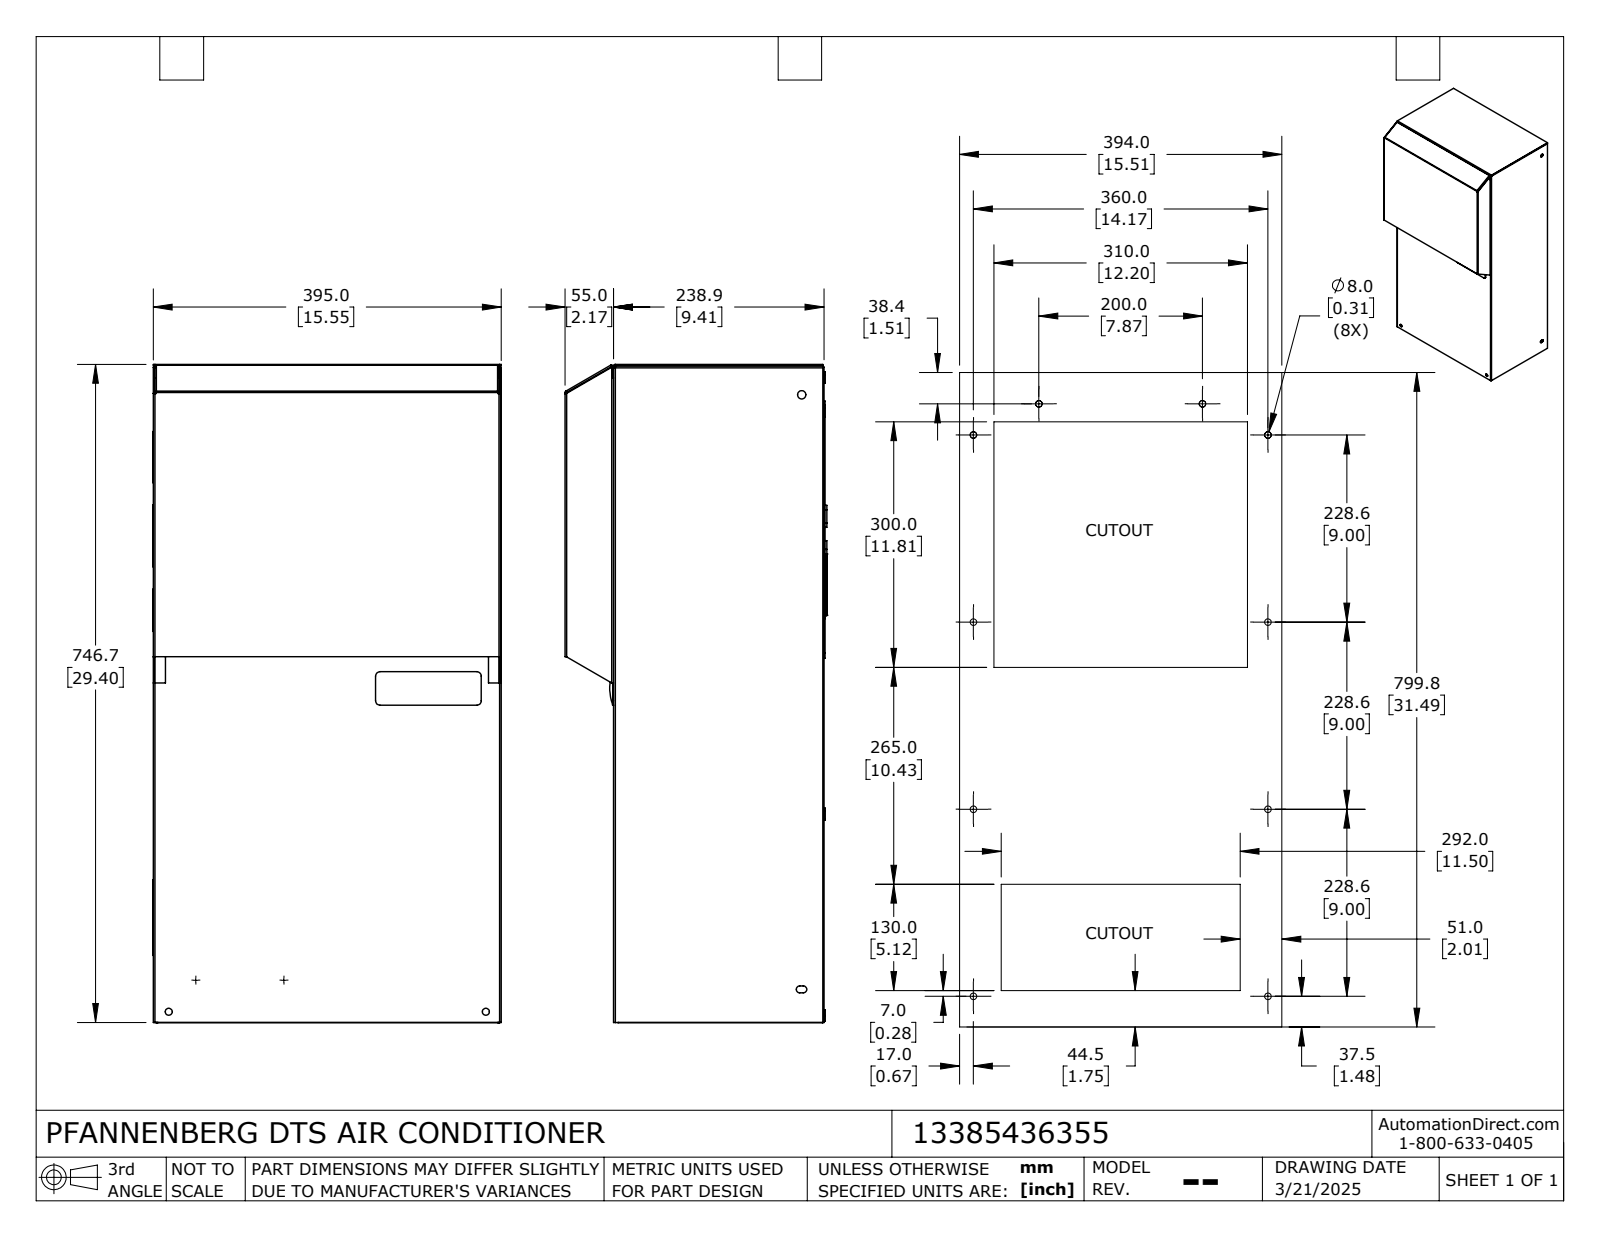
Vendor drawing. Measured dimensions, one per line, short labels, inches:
name: 13385436355_Default
written by: SolidWorks 2024 (CONFIG_CONTROL_DESIGN)
unit: in
bodies: 1 solid, 1498 faces (764 planar, 713 cylindrical, 21 other)
size: 29.397 × 15.571 × 11.698
volume: 4 282 in³; area: 4 274 in²
holes: 19× ⌀0.165, 10× ⌀0.283, 8× ⌀0.163, 6× ⌀0.157, 4× ⌀0.197, 2× ⌀0.236, 2× ⌀0.315, 2× ⌀0.437, 1× ⌀0.118, 1× ⌀0.318, 1× ⌀0.375, 1× ⌀0.825
bosses: 10× ⌀0.512
rounds: 140× R0.125, 129× R0.112, 12× R0.079, 12× R0.197, 11× R0.113, 10× R0.198, 8× R0.031, 8× R0.076
face distances: 0.03, 0.078, 0.048, 9.278, 9.307, 9.355, 0.05, 9.327, 9.357, 9.405
hole spacings: 7.802, 4.398, 5.906, 7.874, 14.744, 26.359, 0.03, 0.035
